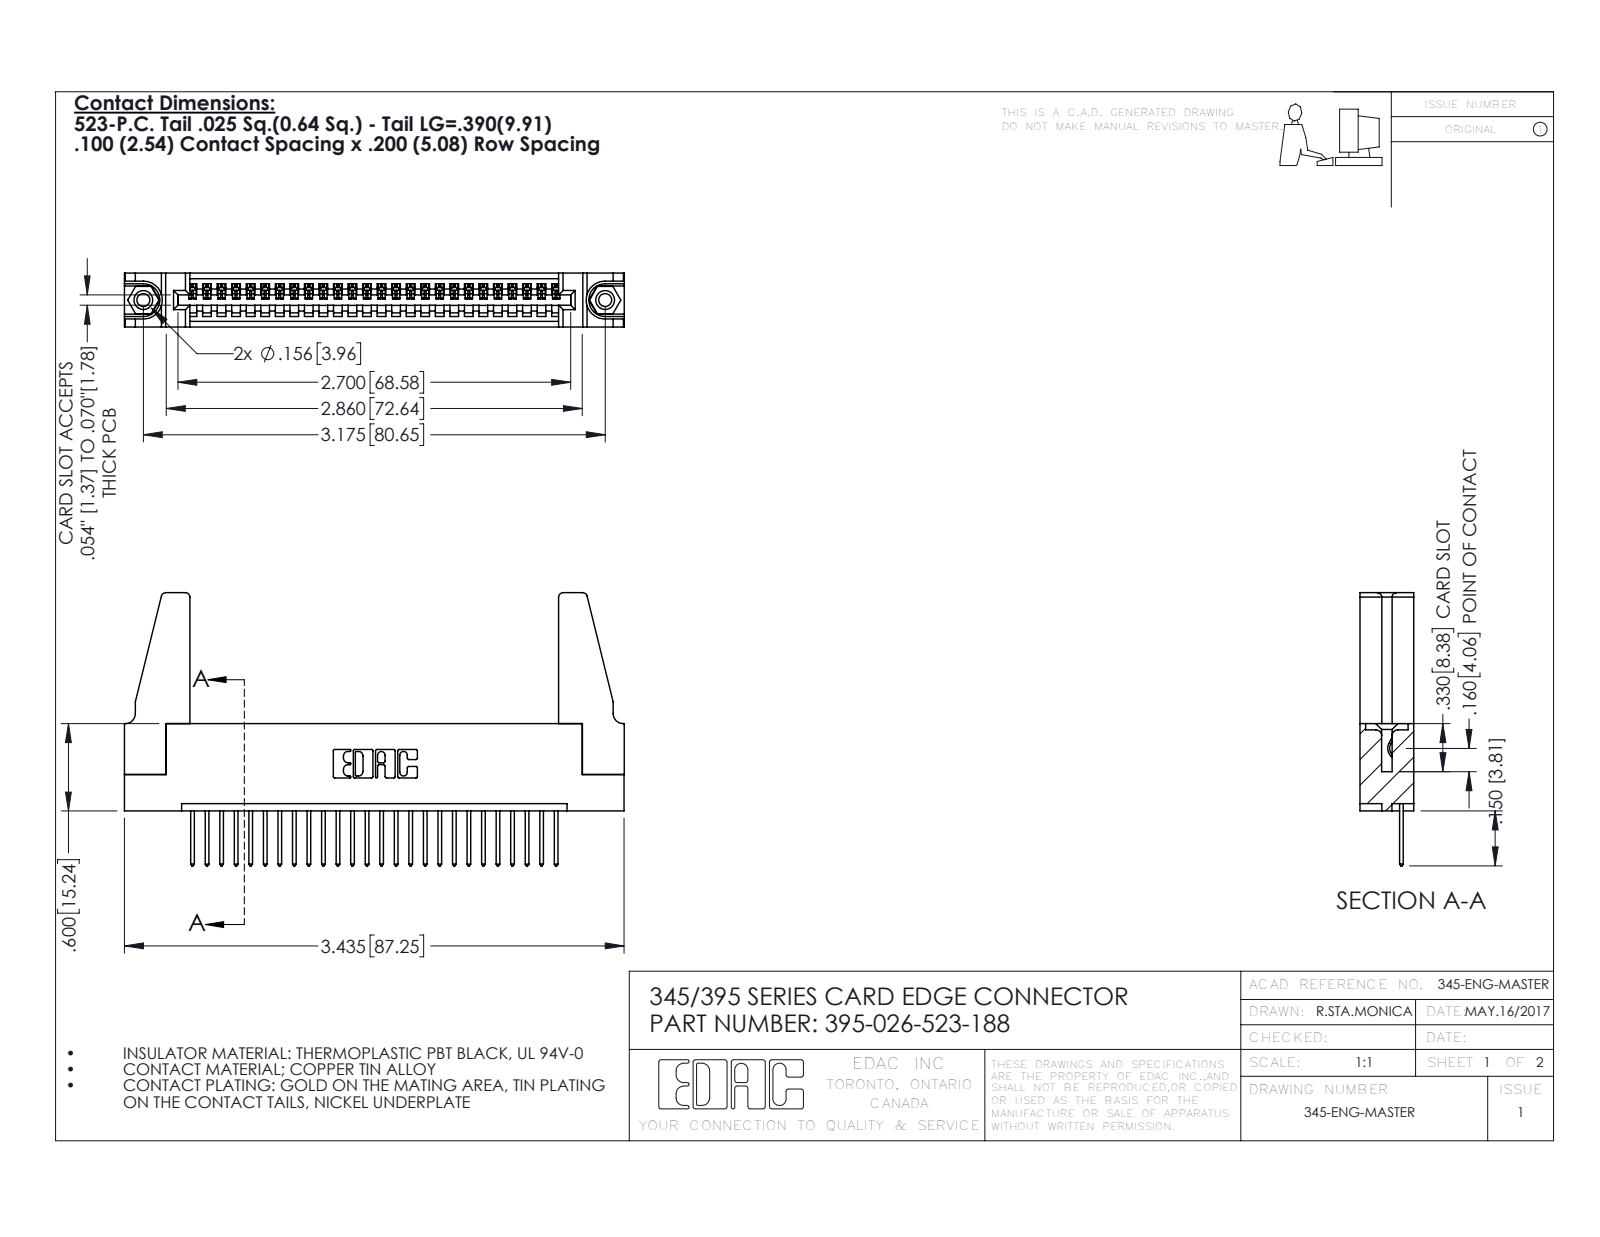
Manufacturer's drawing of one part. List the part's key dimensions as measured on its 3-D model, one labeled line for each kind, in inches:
Part name (STEP PRODUCT): 345-220-078_345-220-088; 345-292-001_345-293-123; 345 Part_Flush Mounting Lugs - 0.156 Dia-TH; 395-026-523-188 (+1 more)
STEP written by: SolidWorks 2016 (CONFIG_CONTROL_DESIGN)
Units: inches
Bodies: 31 solids, 1758 faces (1192 planar, 550 cylindrical, 16 other)
Overall size (bounding box): 3.436 × 1.877 × 0.37
Volume: 0.696 in³ · Surface area: 21.34 in²
Round holes (diameter × count): ⌀0.089 ×2, ⌀0.125 ×2, ⌀0.156 ×2, ⌀0.064 ×1
Round bosses / shafts (diameter × count): ⌀0.155 ×2
Partial cylindrical surfaces — rounded edges, fillets, slot ends (radius × count): R0.006 ×52, R0.01 ×52, R0.01 ×22, R0.03 ×8, R0.007 ×6, R0.031 ×6, R0.026 ×3, R0.031 ×2
Main face-to-face distances: 0.072, 0.37, 0.298, 0.2, 0.098, 0.272, 0.025, 0.225, 0.149, 0.148
Hole centre spacings: 0.27, 2.94, 3.175
